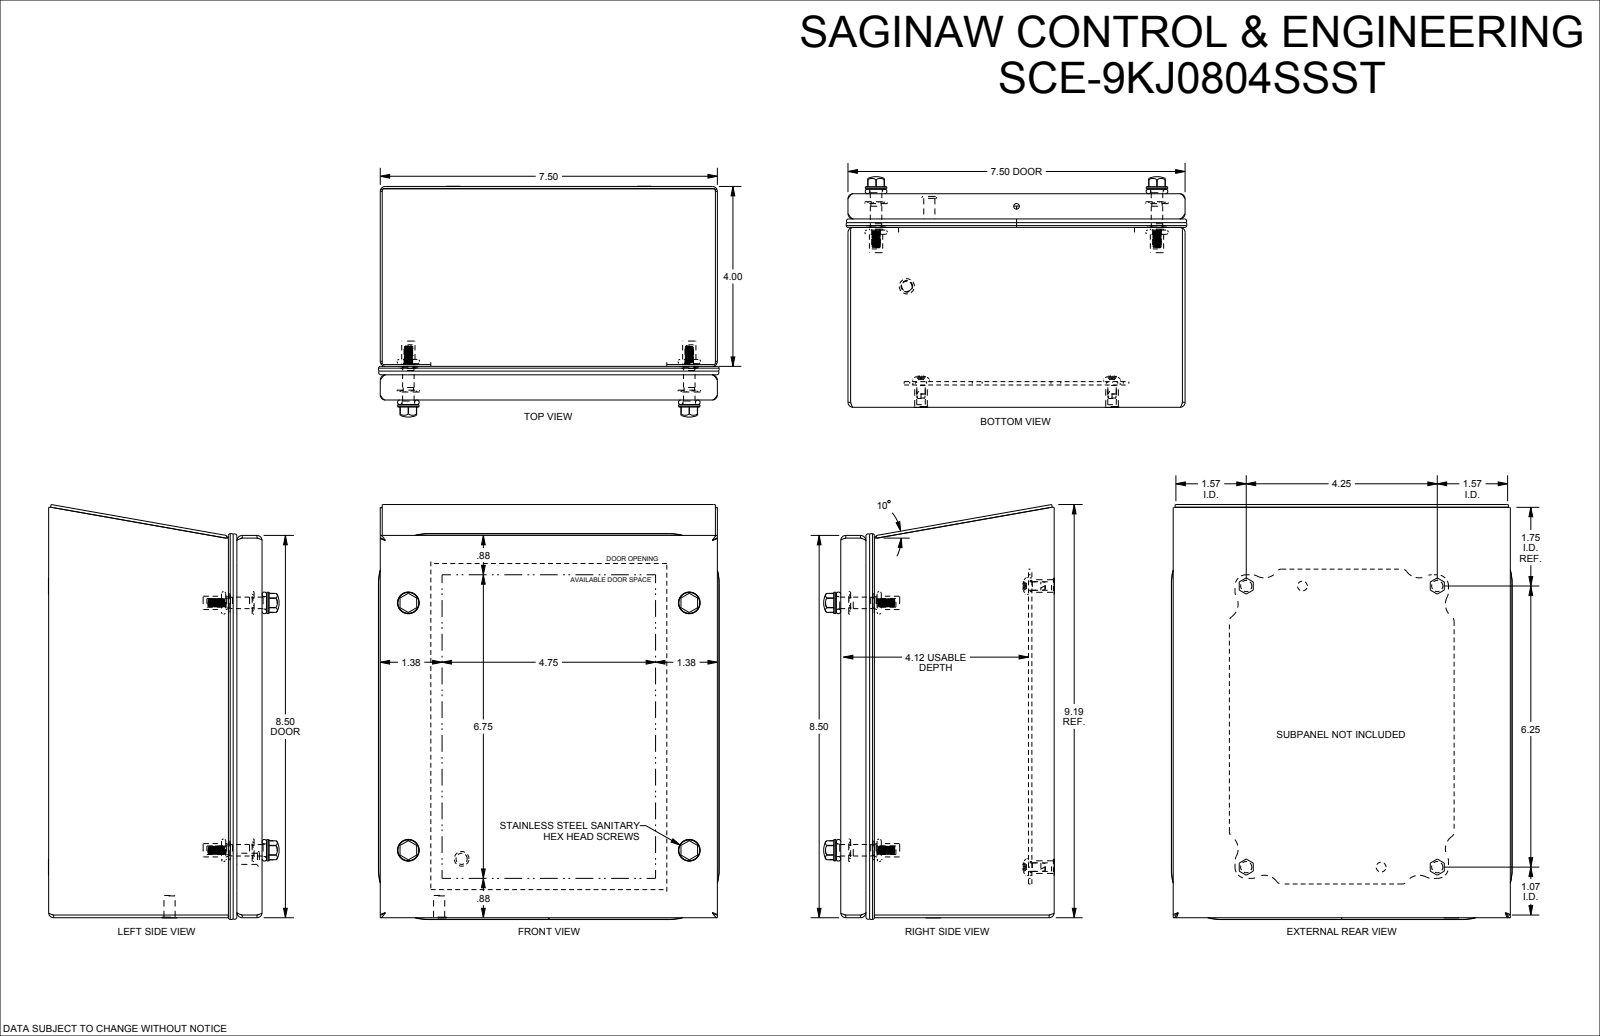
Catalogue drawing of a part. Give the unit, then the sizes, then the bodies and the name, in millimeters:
Units: millimetres
Overall size (bounding box): 233.9 × 192.6 × 130.4
Round holes (diameter × count): ⌀4.8 ×8, ⌀7.1 ×8, ⌀6.4 ×4, ⌀6.9 ×4, ⌀8.1 ×4, ⌀9.3 ×4, ⌀5.5 ×2
Round bosses / shafts (diameter × count): ⌀12.7 ×4, ⌀12.1 ×4, ⌀9.5 ×4, ⌀7.5 ×4, ⌀7.1 ×4, ⌀6.5 ×4, ⌀5.8 ×4, ⌀4.8 ×4
Partial cylindrical surfaces — rounded edges, fillets, slot ends (radius × count): R1.3 ×26, R2.8 ×26, R0.5 ×20, R3.2 ×12, R6.4 ×12, R8.7 ×8, R0.1 ×4, R0.3 ×4
Main face-to-face distances: 1.5, 119.1, 189, 117.6, 120.6, 100.1, 19, 190.5, 187.5, 106.5
Hole centre spacings: 139.7, 158.8, 27.1, 200.1, 133.6, 151.4, 158.6, 200.1
Volume: 472 900 mm³ · Surface area: 545 600 mm²
Bodies: 31 solids, 991 faces (349 planar, 309 cylindrical, 333 other)
Part name (STEP PRODUCT): SCE-9KJ0804SSST
STEP written by: SolidWorks 2021 (AUTOMOTIVE_DESIGN)
